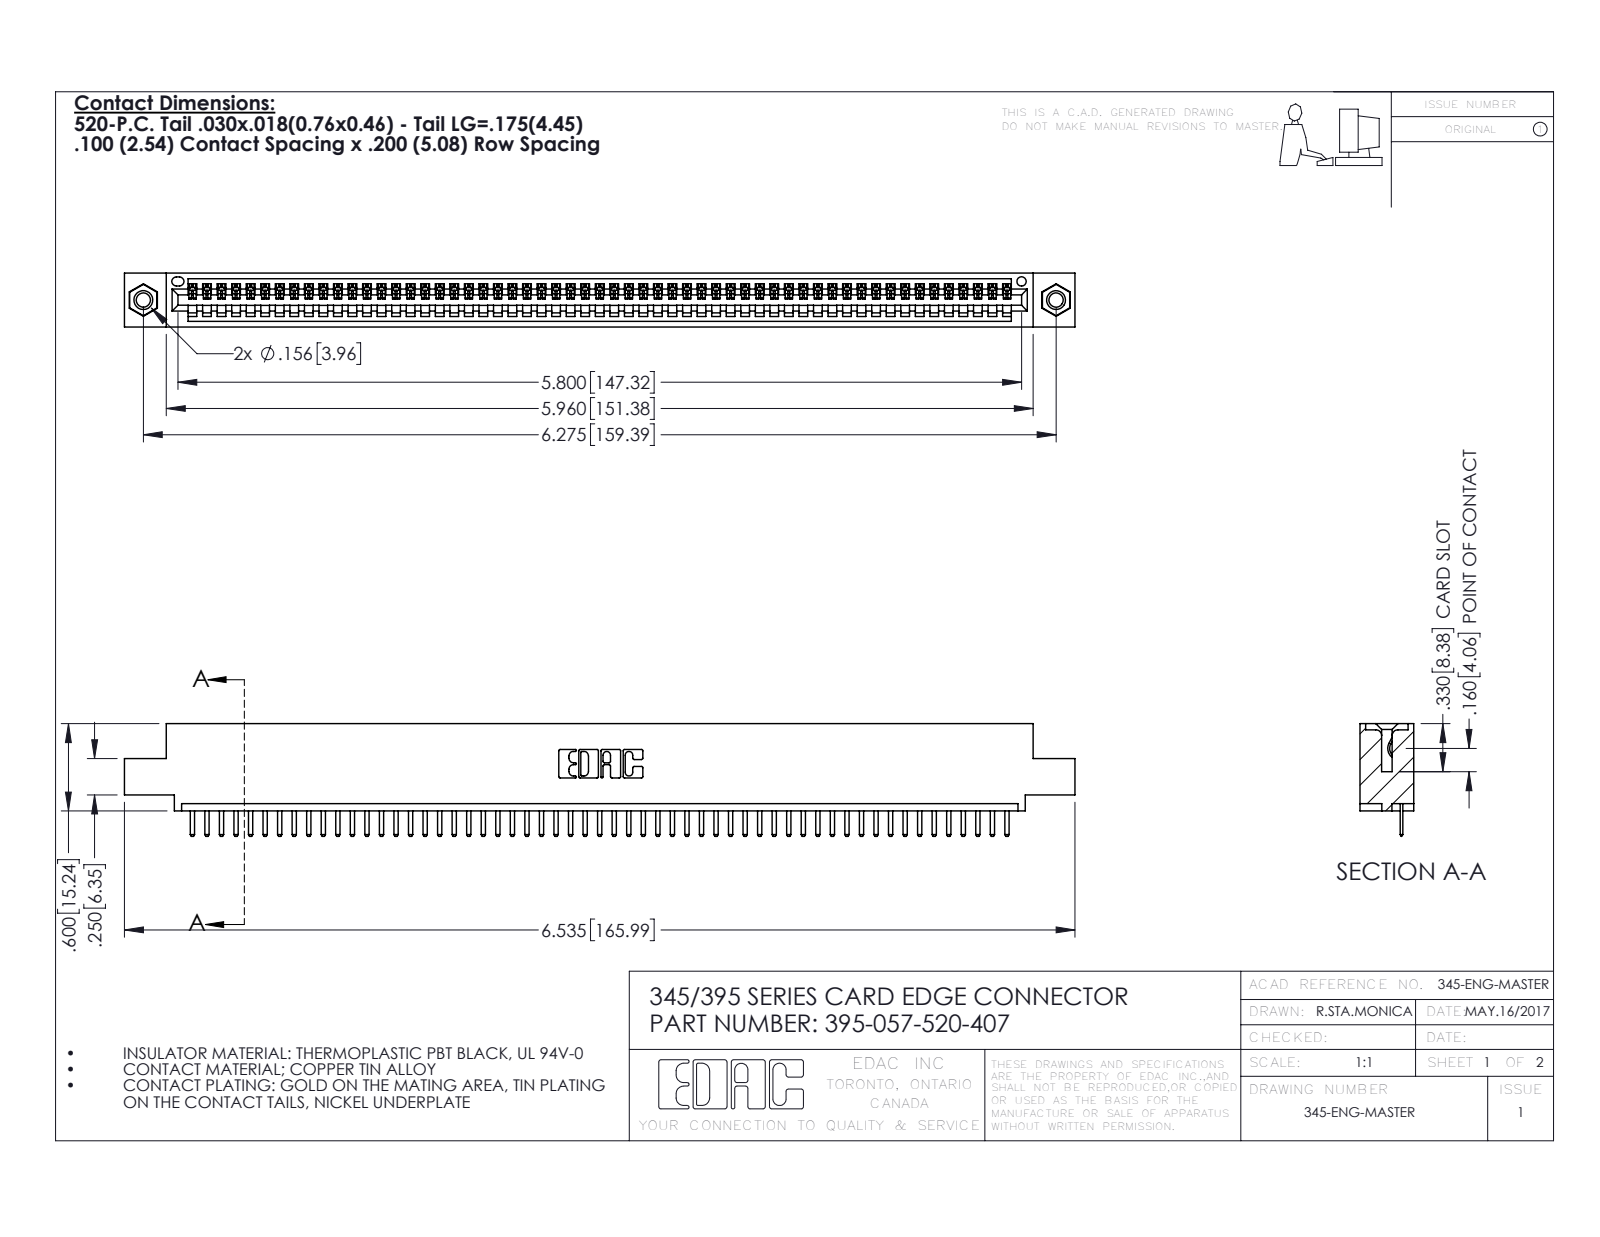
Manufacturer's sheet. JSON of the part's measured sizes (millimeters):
{"part_name": "345-250-001_345-250-005-103; 345-292-001_345-293-120; 345 Part_0.110 Offset - 0.156 Dia-TI; 395-057-520-407", "step_written_by": "SolidWorks 2016 (CONFIG_CONTROL_DESIGN)", "units": "millimeters", "bodies": {"solids": 60, "faces": 3724, "planar": 2510, "cylindrical": 1198, "other": 16}, "overall_size": [166, 19.7, 9.4], "volume_mm3": 15600, "surface_area_mm2": 20560, "round_holes": [[2.5, 2], [3.2, 2], [4, 2], [1.6, 1]], "round_bosses_or_shafts": [[3.9, 2]], "partial_cylinders_radius": [[0.3, 116], [0.2, 114], [0.3, 22], [0.2, 6], [0.8, 6], [0.7, 3], [0.8, 2], [1, 2]], "face_to_face_distances": [1.8, 7.6, 9.4, 5.1, 2.5, 6.9, 0.6, 5.7, 1.8, 3.8], "hole_center_spacings": [6.9, 153.4, 159.4]}
